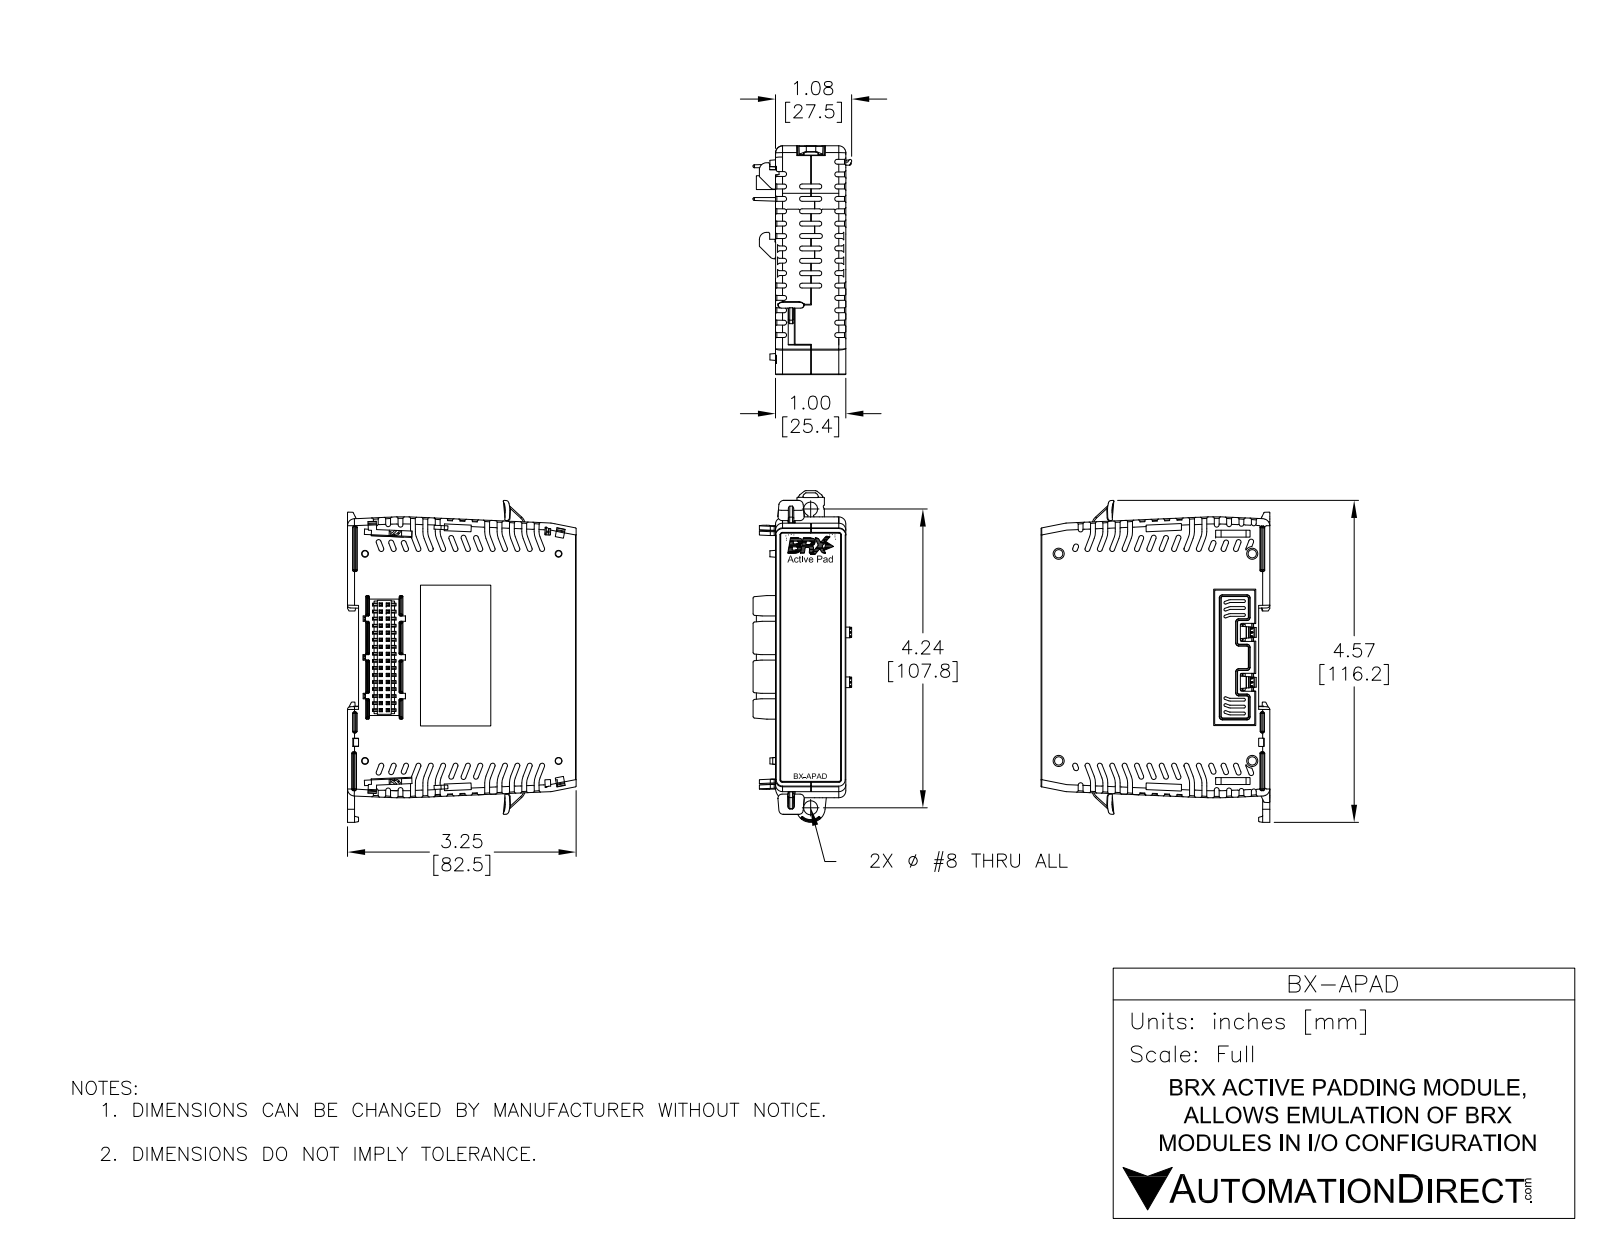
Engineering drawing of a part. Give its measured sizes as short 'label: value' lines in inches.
name: BX-ADAP
written by: SolidWorks 2017 (AUTOMOTIVE_DESIGN)
unit: in
bodies: 3 solids, 3149 faces (2256 planar, 543 cylindrical, 350 other)
size: 4.586 × 3.25 × 1.402
volume: 11.58 in³; area: 72.57 in²
holes: 2× ⌀0.047, 2× ⌀0.065, 2× ⌀0.118, 2× ⌀0.118, 1× ⌀0.199
bosses: 2× ⌀0.062, 2× ⌀0.059
rounds: 102× R0.005, 47× R0.01, 34× R0.02, 24× R0.005, 21× R0.008, 14× R0.117, 13× R0.039, 12× R0.01
face distances: 1, 3.211, 3.22, 0.475, 0.157, 3.053, 3.063, 0.1, 0.078, 0.787
hole spacings: 0.1, 0.824, 0.919, 1.3, 2.093, 2.193, 2.585, 2.617
